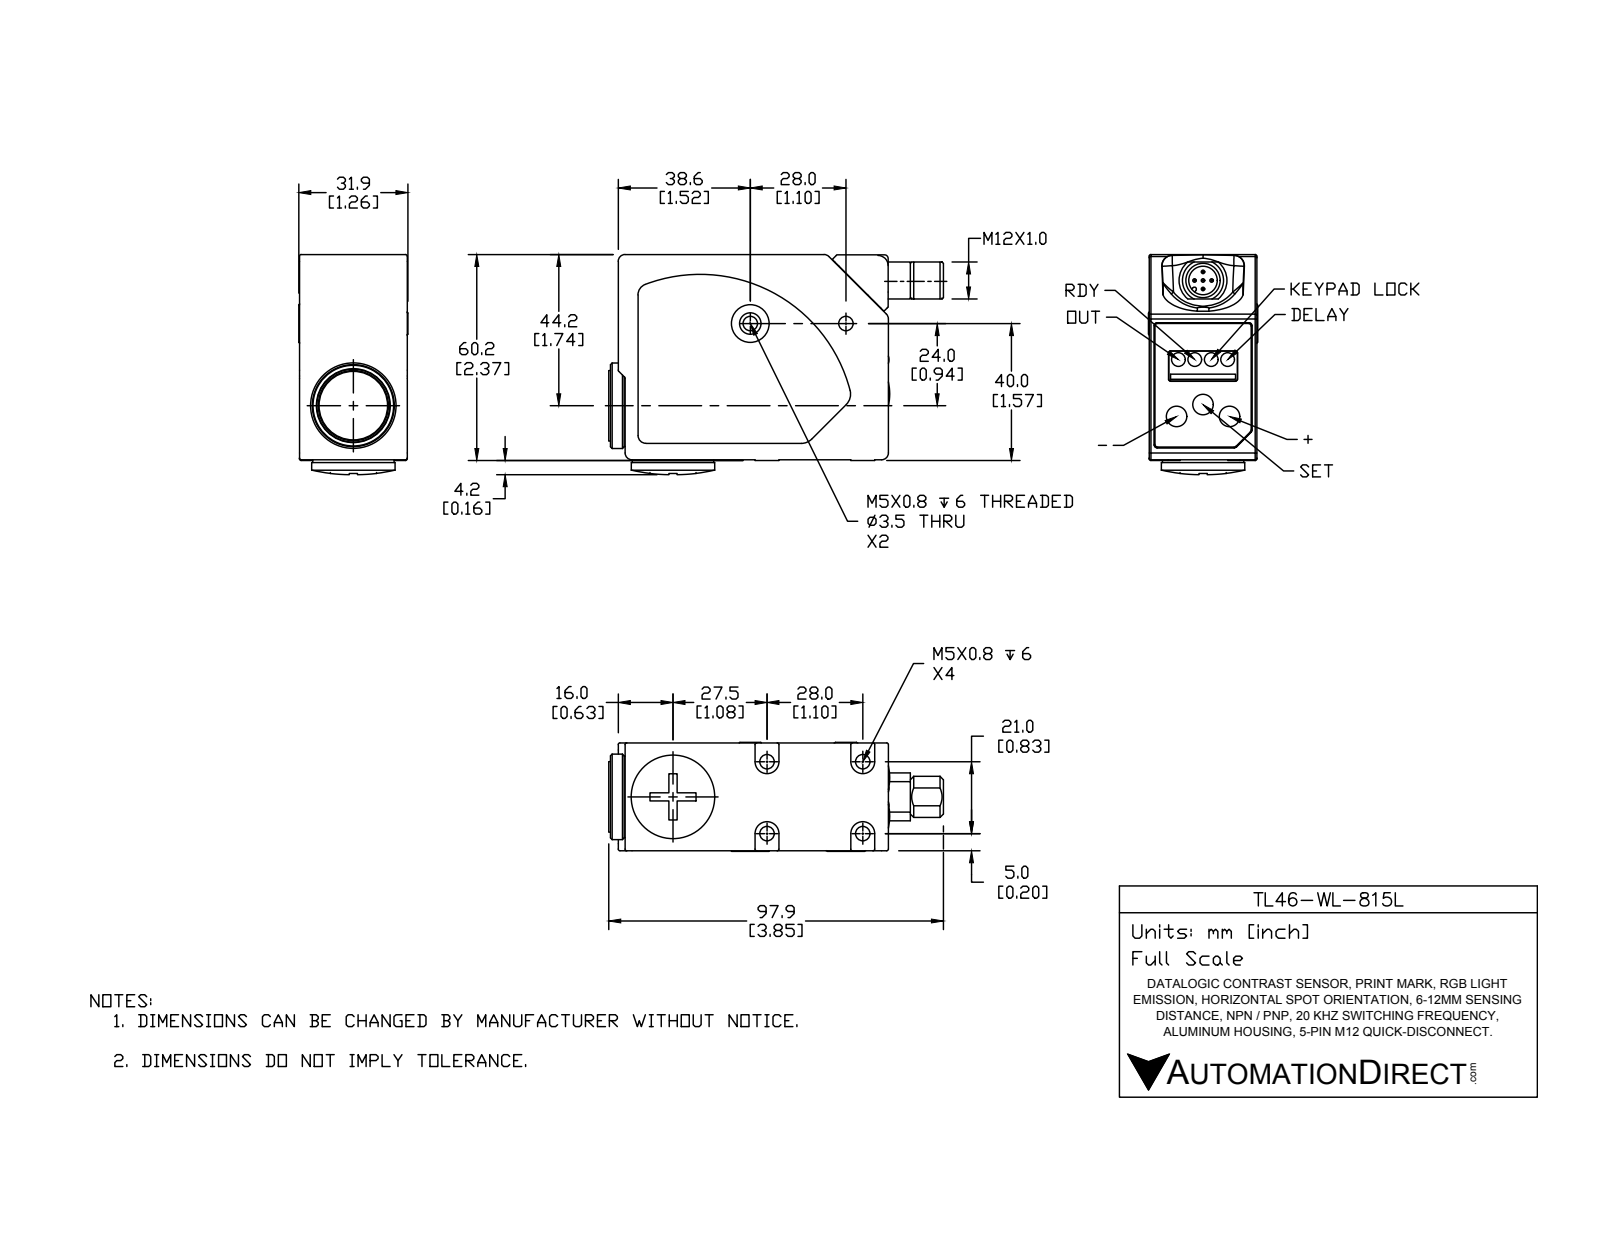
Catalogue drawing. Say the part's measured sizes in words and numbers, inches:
The part is named "TL46-WL-815L". Its 3-D file was written by "SolidWorks 2016 (AUTOMOTIVE_DESIGN)". It is 7 solids with 346 faces: 101 planar, 134 cylindrical and 111 other. Overall it measures 3.854 by 2.534 by 1.256 inches. Its volume is 9.067 cubic inches and its surface area 33.93 square inches. Round holes: 6 of diameter 0.165, 4 of diameter 0.157, 3 of diameter 0.235, 1 of diameter 0.327, 1 of diameter 0.787. Round bosses or shafts: 5 of diameter 0.039, 2 of diameter 0.937, 1 of diameter 0.984, 1 of diameter 0.961, 1 of diameter 0.748, 1 of diameter 0.433. Partial cylindrical surfaces (rounded edges, fillets, slot ends): 32 of radius 0.02, 10 of radius 0.031, 5 of radius 0.024, 5 of radius 0.079, 4 of radius 0.02, 4 of radius 0.138, 1 of radius 0.236, 1 of radius 0.276. The main face-to-face distances are 1.232, 1.224, 1.24, 2.362, 3.11, 0.03, 3.08, 3.031, 3.001, 0.079. The hole center spacings are 0.189, 1.102, 0.378, 0.526, 0.54, 0.59, 0.602, 0.656.
